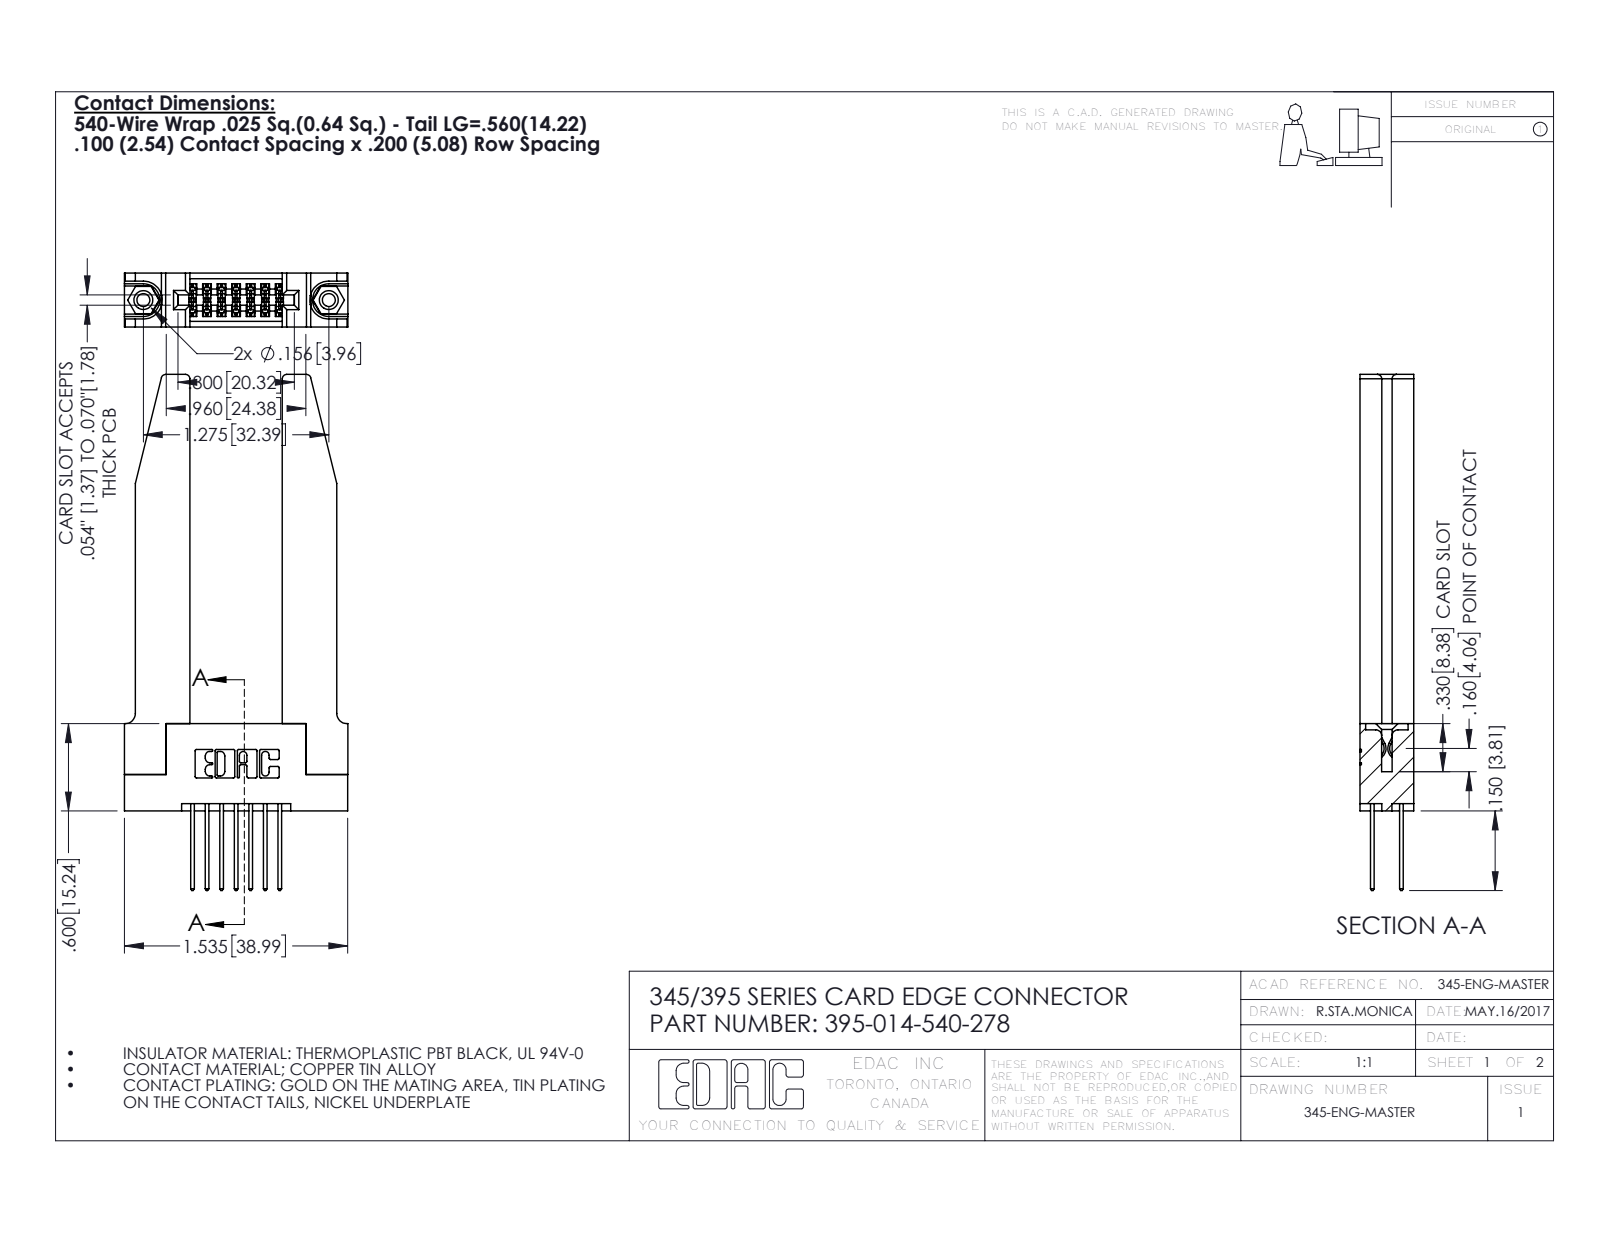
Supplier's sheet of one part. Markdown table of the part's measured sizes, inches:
| quantity | value |
| --- | --- |
| part name | 345 Part_Flush Mounting Lugs - 0.156 Dia-TH; 395-014-540-278; 345-292-001_345-293-140; 345-220-078_345-220-078 (+1 more) |
| STEP written by | SolidWorks 2016 (CONFIG_CONTROL_DESIGN) |
| units | inches |
| bodies | 19 solids, 1060 faces (684 planar, 324 cylindrical, 52 other) |
| overall size | 3.547 × 1.536 × 0.37 |
| volume | 0.689 in³ |
| surface area | 17.99 in² |
| round holes (diameter × count) | 0.089 × 2, 0.125 × 2, 0.156 × 2, 0.064 × 1 |
| round bosses / shafts (diameter × count) | 0.155 × 2 |
| partial cylindrical surfaces (radius × count) | 0.01 × 22, 0.006 × 21, 0.01 × 14, 0.03 × 8, 0.007 × 6, 0.031 × 6, 0.026 × 3, 0.014 × 2 |
| main face-to-face distances | 0.37, 0.072, 0.298, 0.15, 0.148, 0.2, 0.077, 0.22, 0.635, 0.098 |
| hole center spacings | 0.27, 1.045, 1.275 |
